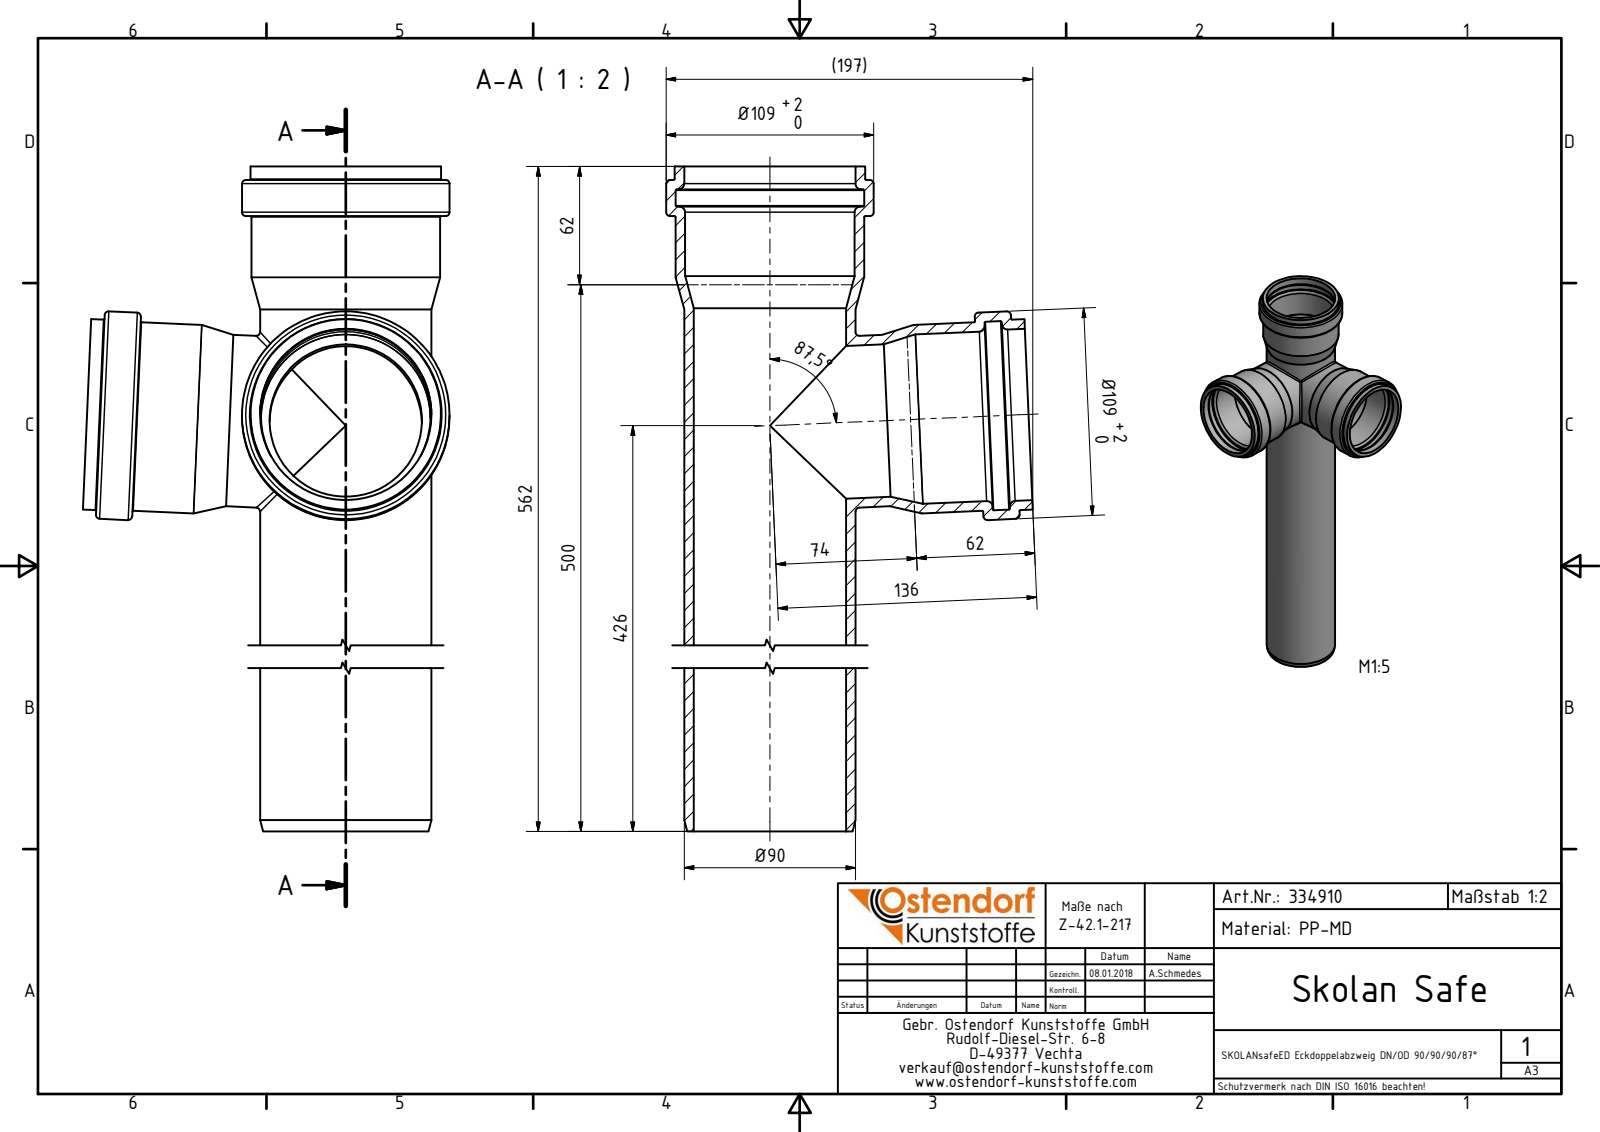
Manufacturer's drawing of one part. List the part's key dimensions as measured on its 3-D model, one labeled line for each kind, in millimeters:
Part name (STEP PRODUCT): 334910 SKOLANsafeED Eckdoppelabzweig DN_OD 90_90_90_87°
STEP written by: Autodesk Inventor 2016 (AUTOMOTIVE_DESIGN)
Units: millimetres
Bodies: 1 solid, 84 faces (16 planar, 24 cylindrical, 44 other)
Overall size (bounding box): 562 × 192.55 × 192.55
Volume: 1 040 000 mm³ · Surface area: 418 873 mm²
Round holes (diameter × count): ⌀80 ×3, ⌀89 ×3, ⌀90 ×3, ⌀99 ×3
Round bosses / shafts (diameter × count): ⌀109 ×3, ⌀100 ×3, ⌀99 ×2, ⌀90 ×2
Main face-to-face distances: 26, 5, 14, 19, 7, 21, 9, 12, 562, 536
